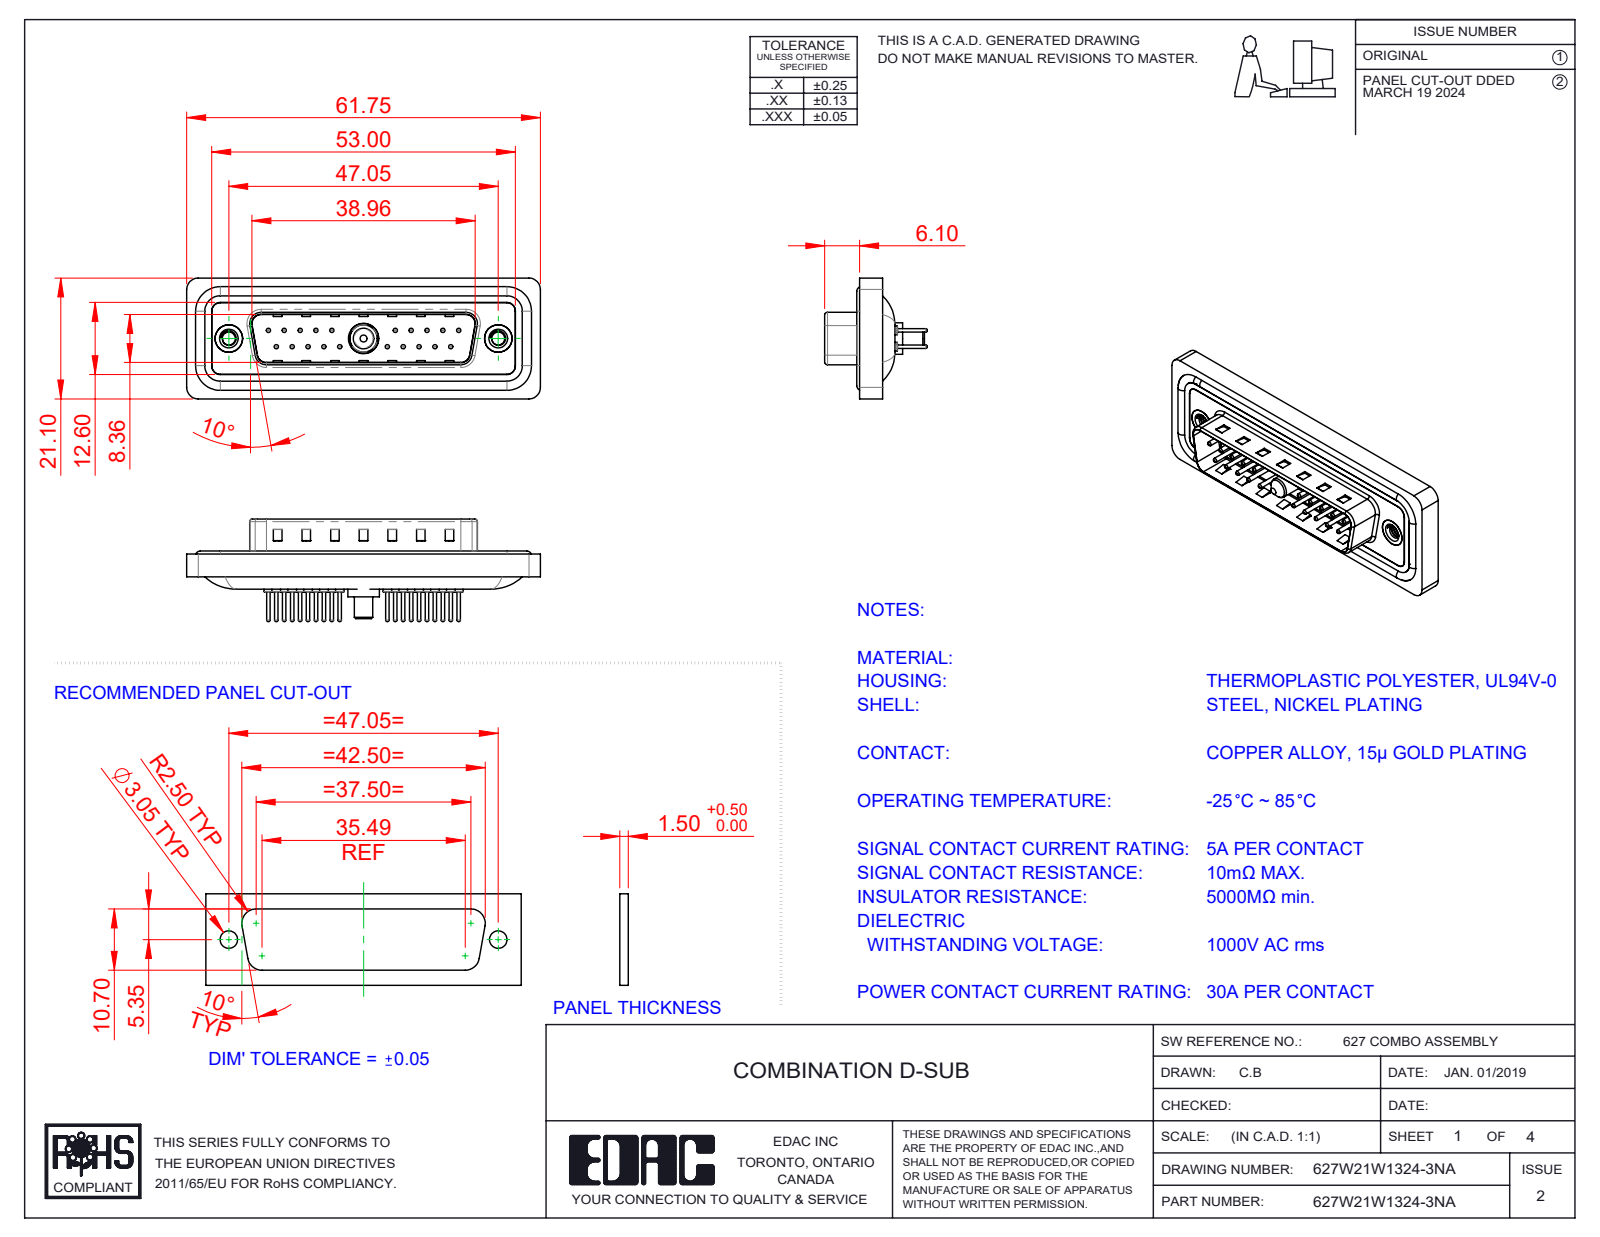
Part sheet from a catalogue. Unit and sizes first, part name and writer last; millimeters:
Units: millimetres
Overall size (bounding box): 61.75 × 21.1 × 17.9
Round holes (diameter × count): ⌀0.75 ×20, ⌀1.6 ×20, ⌀2 ×20, ⌀2.26 ×2, ⌀4 ×2, ⌀4.8 ×2, ⌀5 ×2, ⌀4.85 ×1, ⌀5.3 ×1
Round bosses / shafts (diameter × count): ⌀1.5 ×20, ⌀0.6 ×20, ⌀1.6 ×4, ⌀4.9 ×2, ⌀5.5 ×1, ⌀5.2 ×1, ⌀4.75 ×1, ⌀3.75 ×1
Partial cylindrical surfaces — rounded edges, fillets, slot ends (radius × count): R1.5 ×22, R2 ×18, R0.5 ×8, R1.6 ×8, R0.25 ×4, R0.6 ×4, R0.65 ×4, R0.9 ×4
Main face-to-face distances: 0.4, 1.5, 1.1, 1.6, 0.5, 3.1, 2.9, 4.1, 0.82, 9.58
Hole centre spacings: 3.16, 2.77, 5.54, 8.31, 5.04, 19.39, 20.97, 22.16
Volume: 7 206 mm³ · Surface area: 11 955 mm²
Bodies: 29 solids, 1260 faces (359 planar, 489 cylindrical, 412 other)
Part name (STEP PRODUCT): 627Combo Shell Front_25 Contacts; 627Combo Shell Rear_25 Contacts; 627Combo Waterproof Housing_25 Contacts; 627W21W1324-3NA (+5 more)
STEP written by: SolidWorks 2023 (CONFIG_CONTROL_DESIGN)
